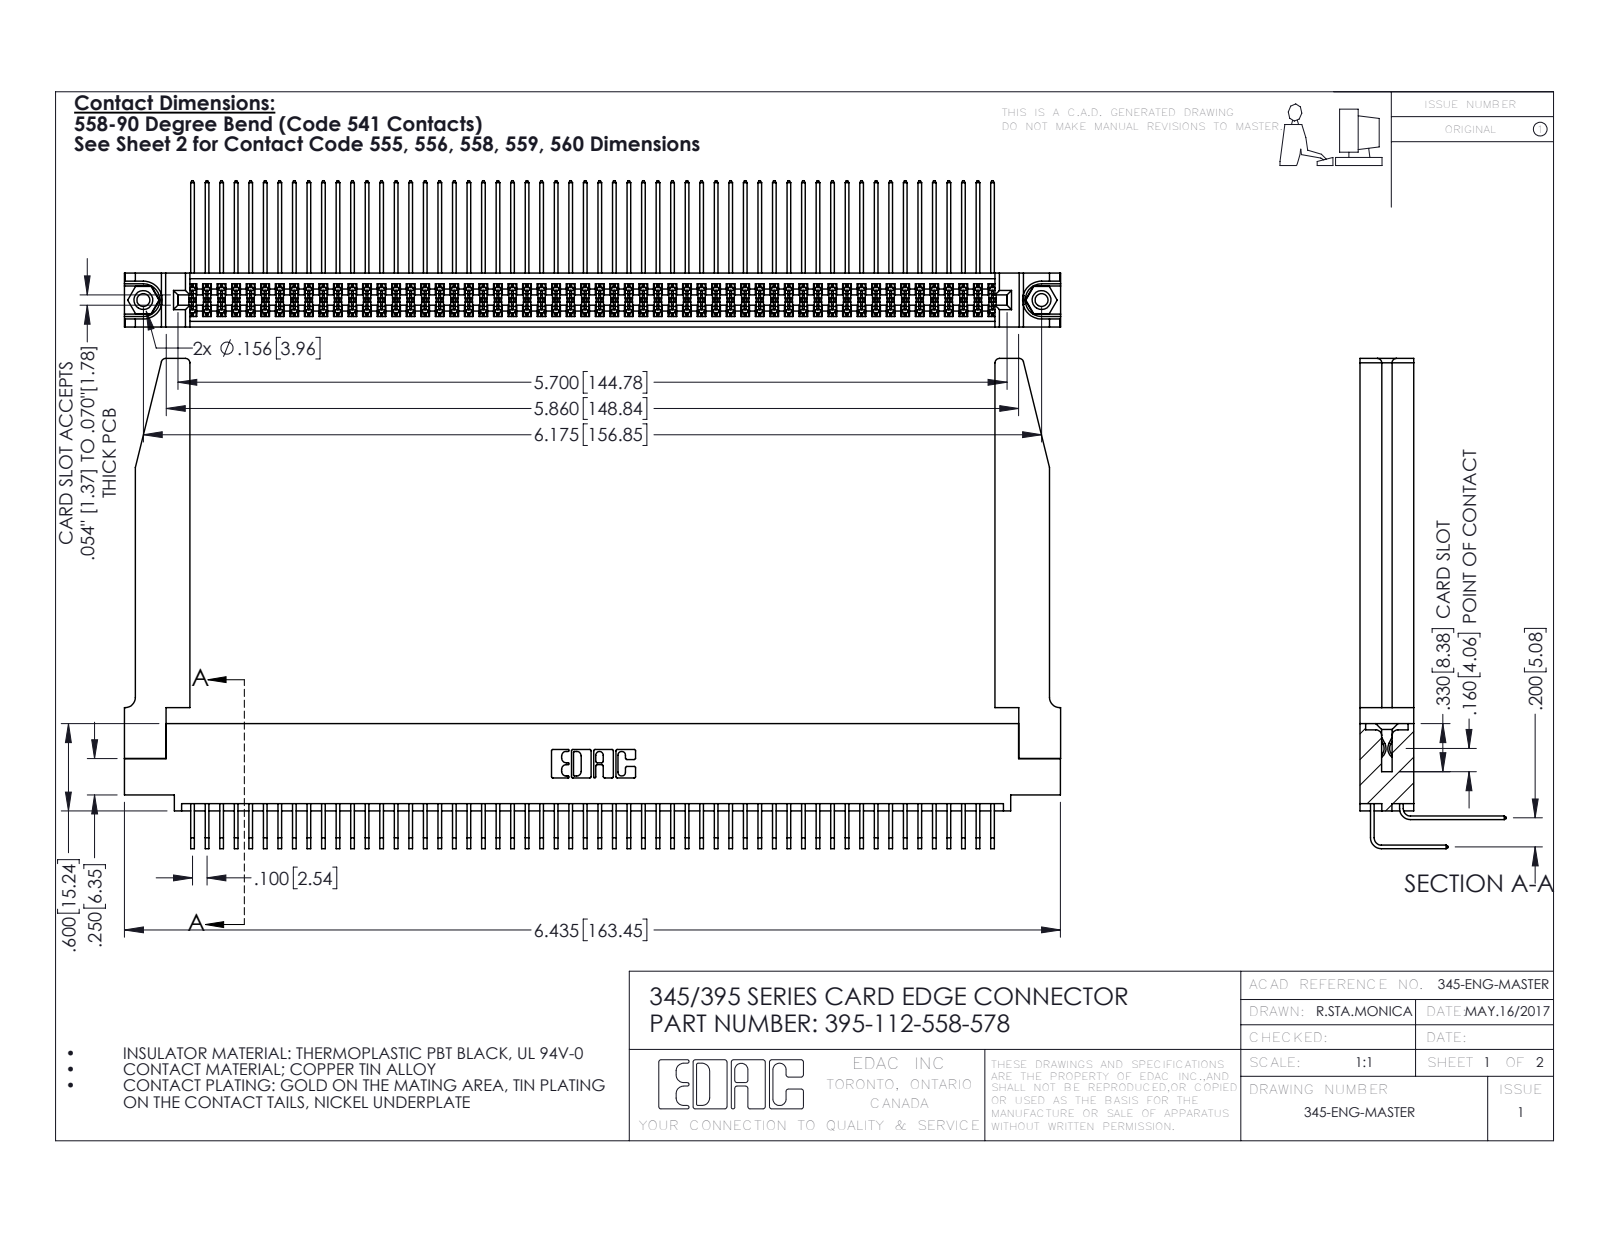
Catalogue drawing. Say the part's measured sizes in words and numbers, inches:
The part is named "345-292-001_558 Tail - 2; 345-292-001_558 559 Tail - 1; 345-220-078_345-220-078; 345 Part_0.110 Offset - 0.156 Dia-TH (+2 more)". Its 3-D file was written by "SolidWorks 2016 (CONFIG_CONTROL_DESIGN)". It is 117 solids with 6188 faces: 4146 planar, 1990 cylindrical and 52 other. Overall it measures 6.436 by 3.369 by 1.005 inches. Its volume is 1.486 cubic inches and its surface area 53.87 square inches. Round holes: 2 of diameter 0.089, 2 of diameter 0.125, 2 of diameter 0.156, 1 of diameter 0.064. Round bosses or shafts: 2 of diameter 0.155. Partial cylindrical surfaces (rounded edges, fillets, slot ends): 169 of radius 0.006, 22 of radius 0.01, 8 of radius 0.03, 6 of radius 0.007, 6 of radius 0.031, 3 of radius 0.026, 2 of radius 0.014, 2 of radius 0.019. The main face-to-face distances are 0.072, 0.298, 0.37, 0.2, 0.098, 0.272, 0.025, 0.225, 0.025, 0.175. The hole center spacings are 0.27, 5.939, 6.175.
